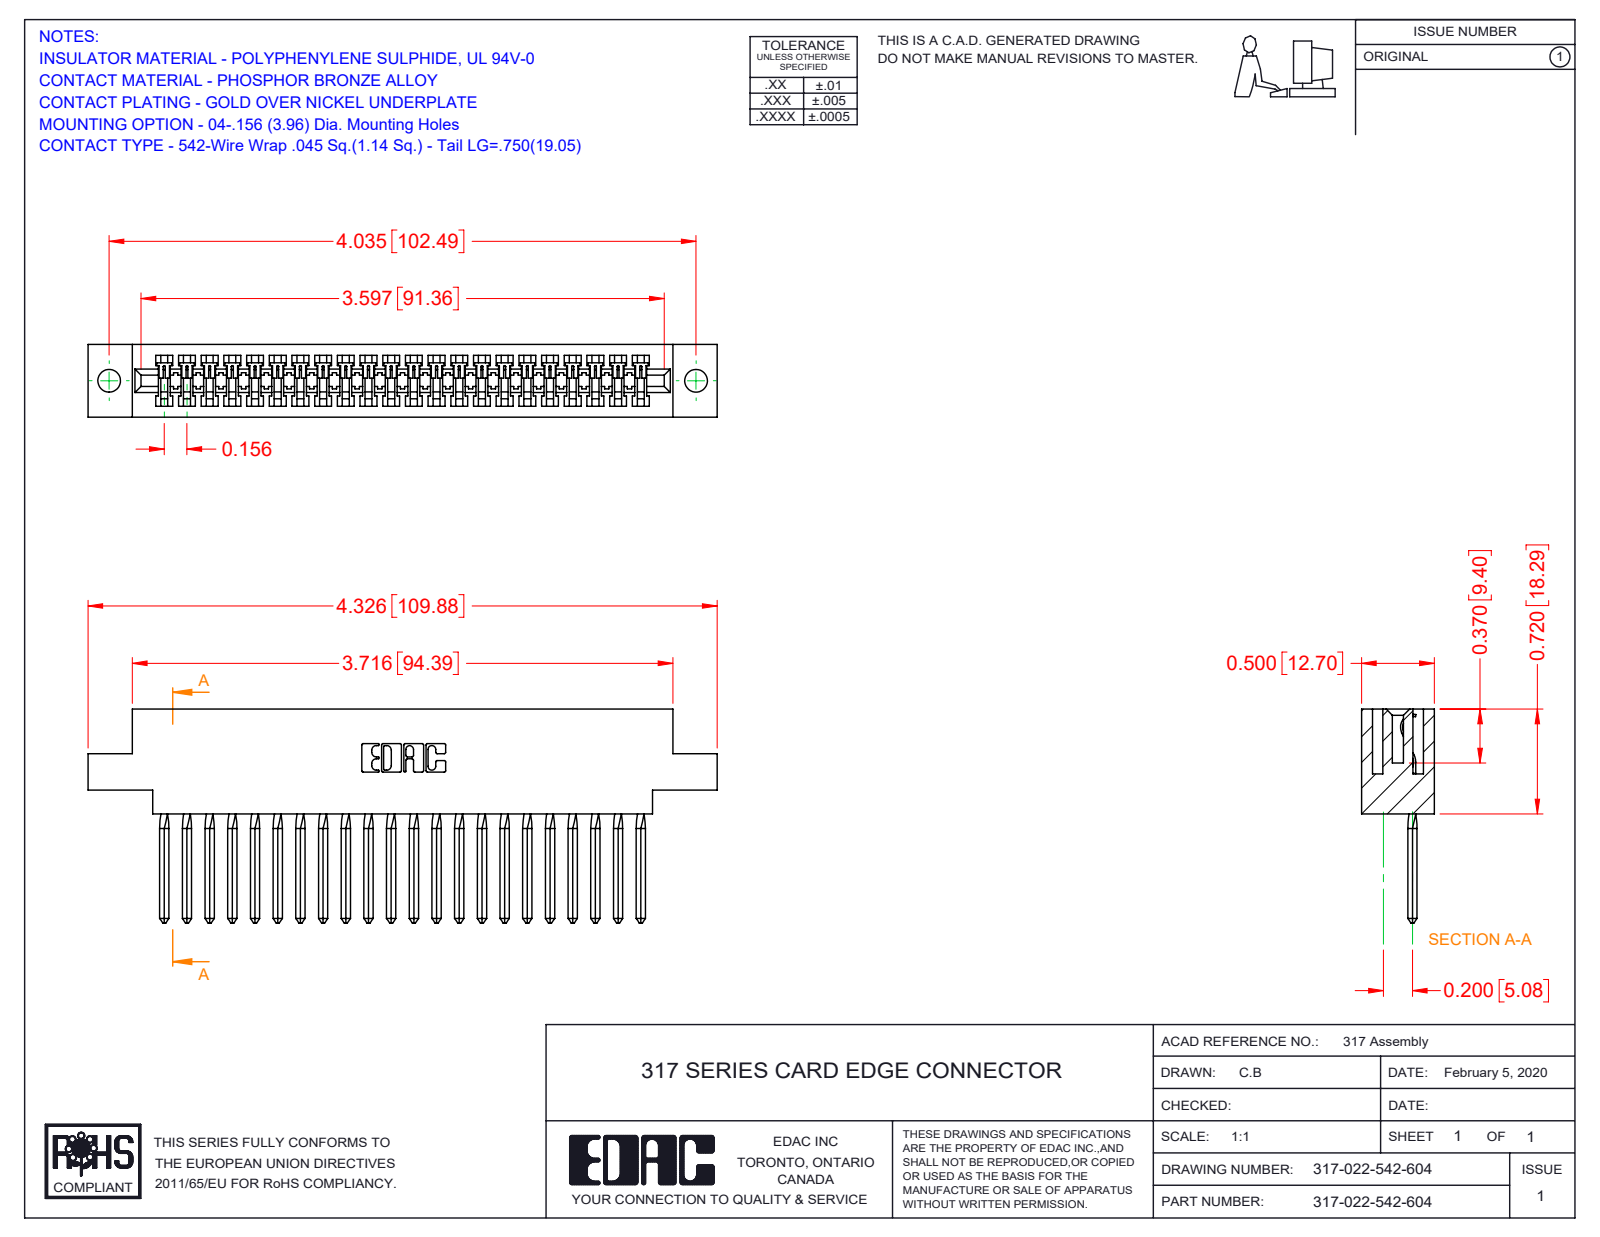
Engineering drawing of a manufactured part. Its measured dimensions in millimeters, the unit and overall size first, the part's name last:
Units: millimetres
Overall size (bounding box): 109.9 × 37.3 × 12.7
Round holes (diameter × count): ⌀4 ×2
Partial cylindrical surfaces — rounded edges, fillets, slot ends (radius × count): R0.2 ×44, R0.3 ×22, R0.2 ×6, R0.8 ×6, R0.7 ×3, R1.9 ×1, R2.3 ×1, R2.5 ×1
Main face-to-face distances: 12.7, 1.9, 10.8, 8.9, 2.8, 3.5, 18.3, 5.4, 7.3, 5.4
Hole centre spacings: 102.5
Volume: 16 400 mm³ · Surface area: 19 300 mm²
Bodies: 23 solids, 1752 faces (1466 planar, 198 cylindrical, 88 other)
Part name (STEP PRODUCT): 317-022-542-604; 317 Part_.156 Dia - TH; 317-290-003_542
STEP written by: SolidWorks 2016 (CONFIG_CONTROL_DESIGN)
